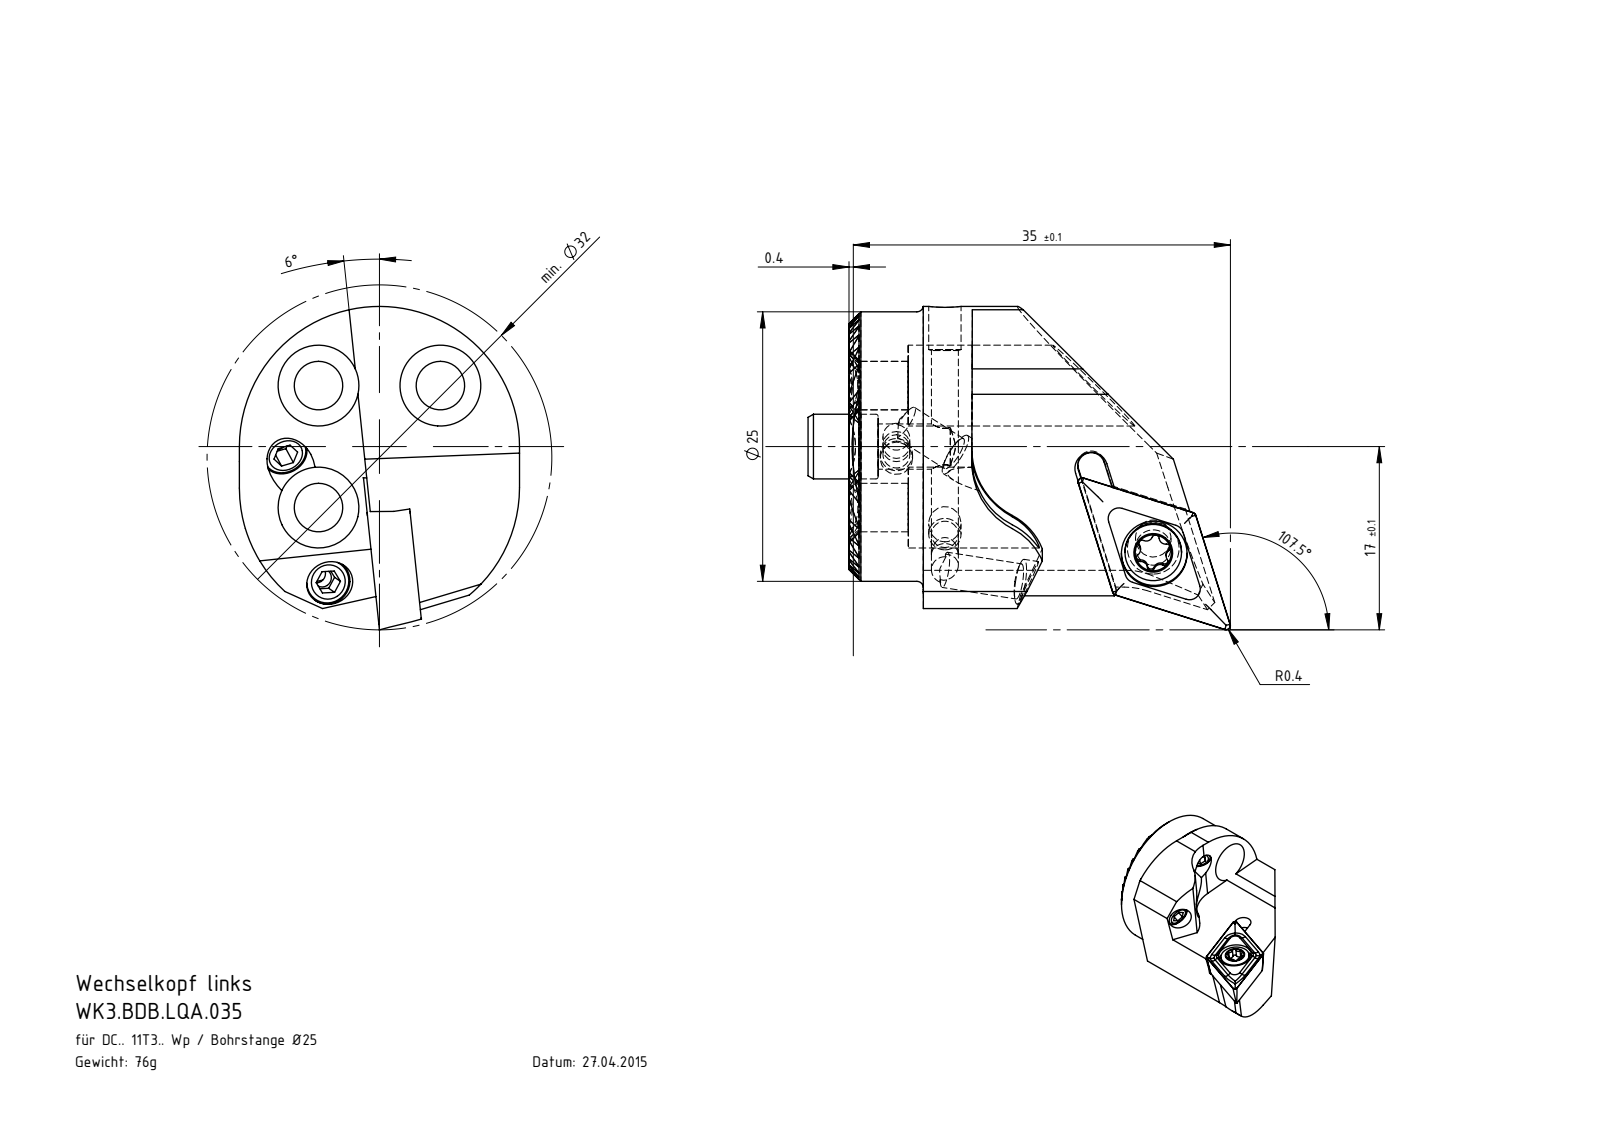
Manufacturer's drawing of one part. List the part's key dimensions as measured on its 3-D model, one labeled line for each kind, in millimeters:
Part name (STEP PRODUCT): WK3.BDB.LQA.035; DCMT11T304; KVT_MB_600_030; WKX-ER1.004.005_A_PreviewCfg (+2 more)
STEP written by: SolidWorks 2017 (AUTOMOTIVE_DESIGN)
Units: millimetres
Bodies: 11 solids, 500 faces (179 planar, 159 cylindrical, 162 other)
Overall size (bounding box): 39.2 × 30.01 × 26
Volume: 9 306 mm³ · Surface area: 6 213 mm²
Round holes (diameter × count): ⌀2.38 ×3, ⌀2.5 ×3, ⌀3.3 ×3, ⌀4.2 ×3, ⌀4.5 ×3, ⌀7.5 ×3, ⌀1.7 ×2, ⌀3 ×2, ⌀4.4 ×1, ⌀6 ×1, ⌀6.1 ×1
Round bosses / shafts (diameter × count): ⌀3 ×3, ⌀4 ×2, ⌀25 ×1
Partial cylindrical surfaces — rounded edges, fillets, slot ends (radius × count): R0.12 ×20, R13 ×3, R7 ×2, R1.25 ×1, R6 ×1
Main face-to-face distances: 4.33, 1.08, 3.25, 5.41, 8.66, 7.58, 2.16, 2.17, 3.66, 9.74
Hole centre spacings: 8, 11.32, 16.01
